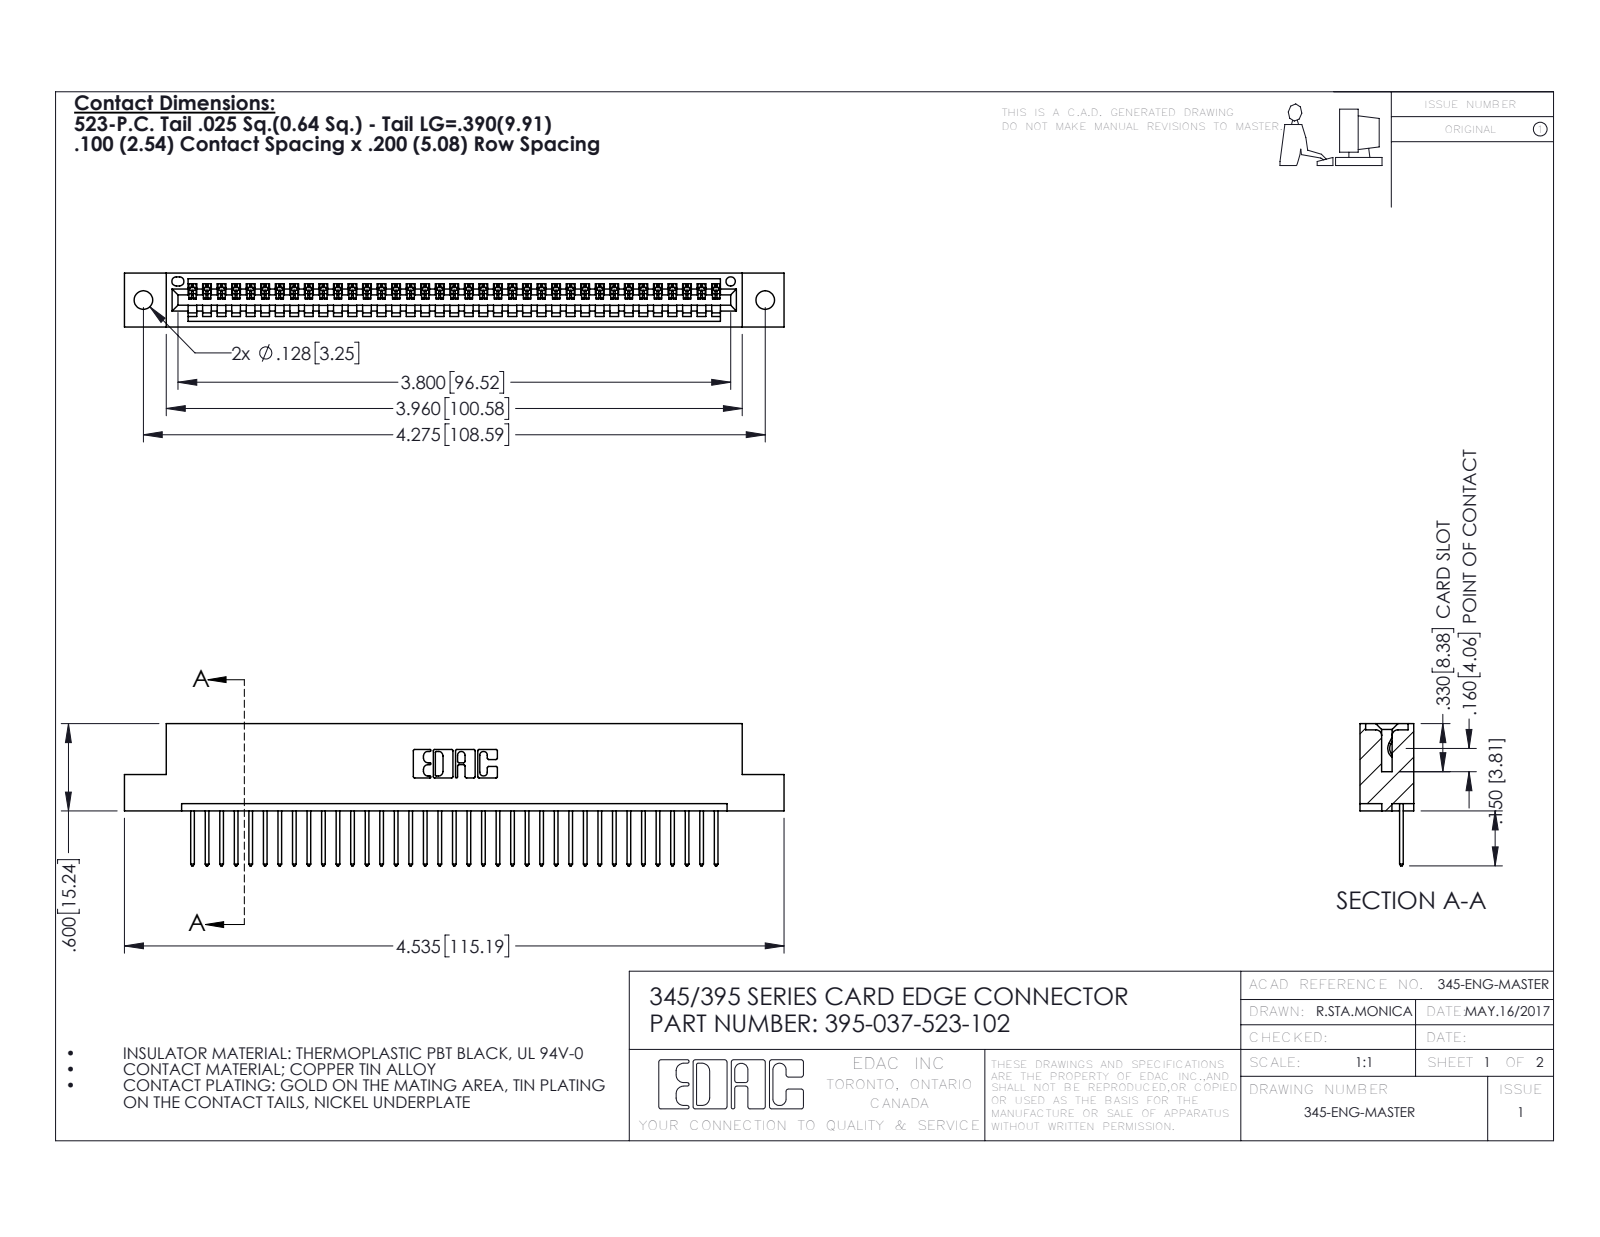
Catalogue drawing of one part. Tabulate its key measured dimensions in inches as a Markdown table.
| quantity | value |
| --- | --- |
| part name | 395-037-523-102; 345-292-001_345-293-123; 345 Part_Flush Mounting Lugs - 0.128 Dia |
| STEP written by | SolidWorks 2016 (CONFIG_CONTROL_DESIGN) |
| units | inches |
| bodies | 38 solids, 2272 faces (1560 planar, 712 cylindrical, 0 other) |
| overall size | 4.535 × 0.977 × 0.37 |
| volume | 0.662 in³ |
| surface area | 21.88 in² |
| round holes (diameter × count) | 0.128 × 2, 0.064 × 1 |
| partial cylindrical surfaces (radius × count) | 0.006 × 74, 0.01 × 74, 0.01 × 22, 0.007 × 6, 0.031 × 6, 0.026 × 3, 0.031 × 2, 0.04 × 2 |
| main face-to-face distances | 0.298, 0.072, 0.2, 0.37, 0.098, 0.272, 0.025, 0.225, 0.149, 0.072 |
| hole center spacings | 0.27, 4.039, 4.275 |
